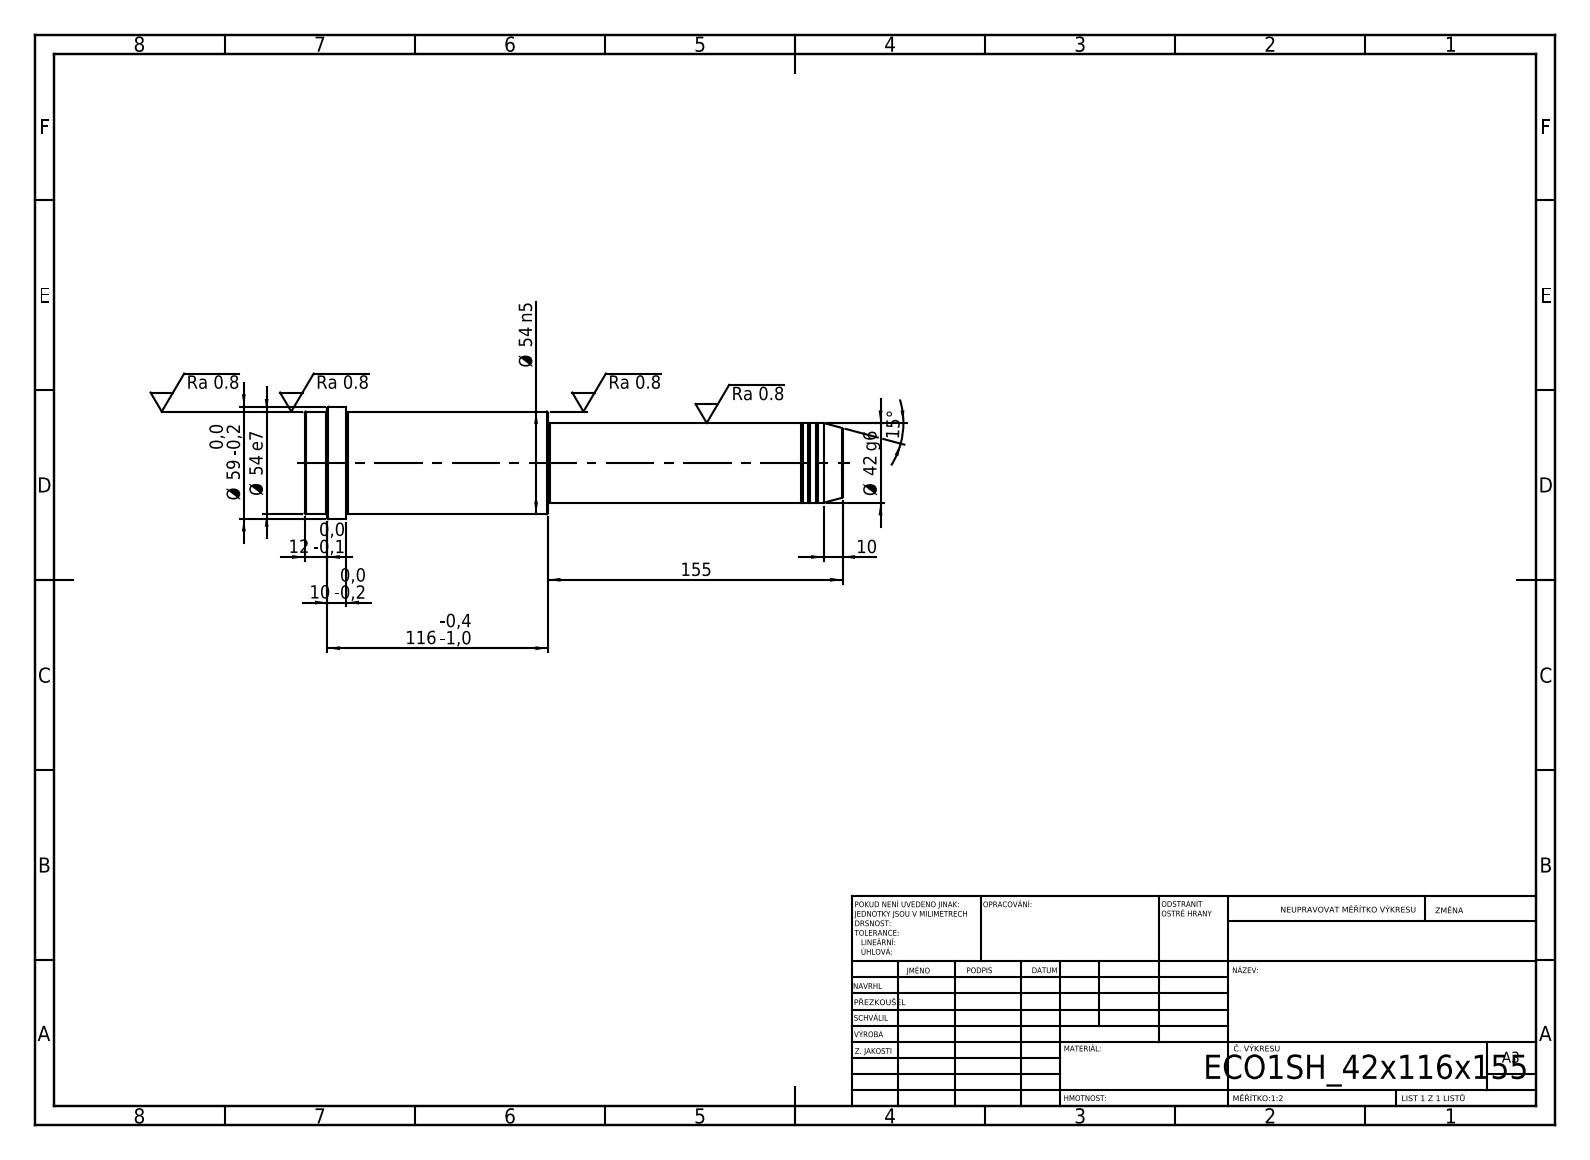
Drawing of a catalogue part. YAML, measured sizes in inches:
step_written_by: "SolidWorks 2019 (CONFIG_CONTROL_DESIGN)"
units: inches
bodies: {solids: 1, faces: 52, planar: 6, cylindrical: 16, other: 30}
overall_size: [11.142, 2.323, 2.323]
volume: 31.14
surface_area: 74.06
round_bosses_or_shafts:
  - {diameter: 2.323, count: 1}
  - {diameter: 2.126, count: 1}
  - {diameter: 1.654, count: 1}
  - {diameter: 1.614, count: 1}
face_to_face_distances: [11.142, 6.102, 5.039, 10.276, 4.173, 0.866, 10.669, 4.567, 0.394, 0.472]
